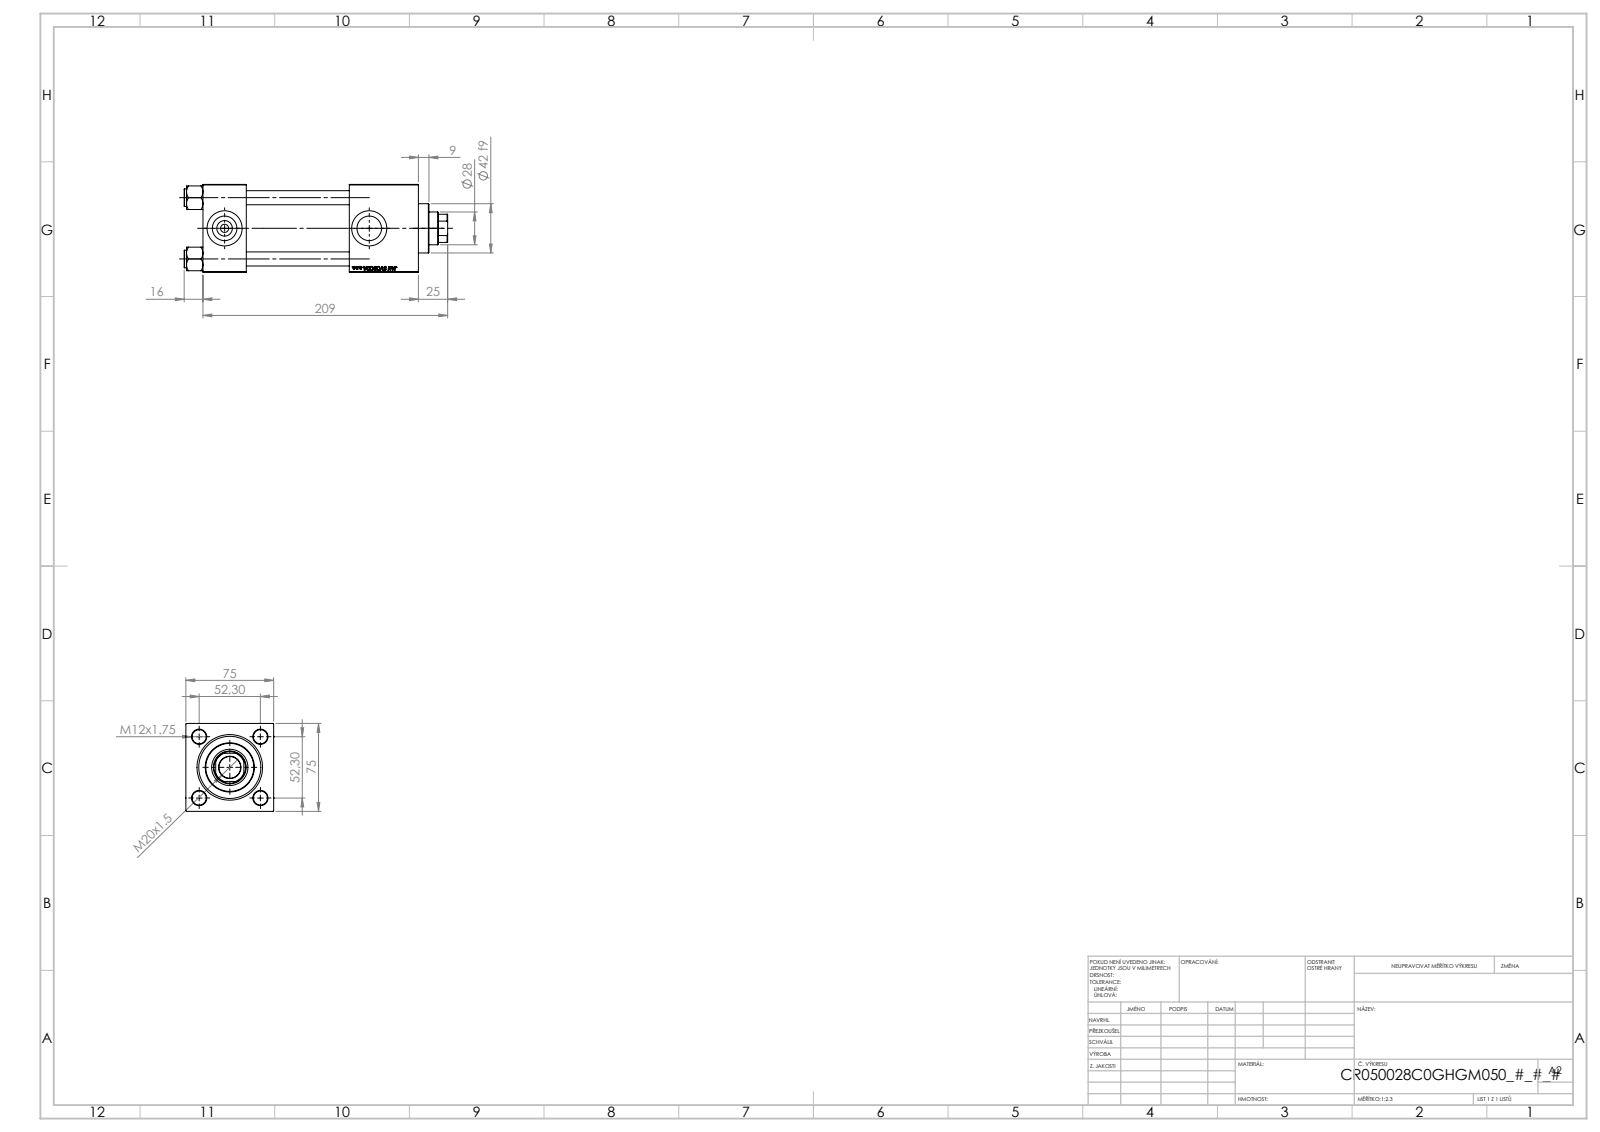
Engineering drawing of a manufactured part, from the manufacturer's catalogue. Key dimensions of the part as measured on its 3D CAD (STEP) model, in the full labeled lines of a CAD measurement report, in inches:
Part name (STEP PRODUCT): V215CR_C_Body; V215CR_C_TYCINKA; V215CR_VCP_C; V215_VC_A (+1 more)
STEP written by: SolidWorks 2019 (CONFIG_CONTROL_DESIGN)
Units: inches
Bodies: 11 solids, 1148 faces (526 planar, 86 cylindrical, 536 other)
Overall size (bounding box): 8.858 × 2.974 × 2.953
Volume: 43.7 in³ · Surface area: 260.5 in²
Round holes (diameter × count): ⌀0.472 ×4, ⌀0.276 ×2, ⌀0.825 ×2, ⌀1.181 ×2, ⌀0.728 ×1, ⌀1.102 ×1, ⌀1.22 ×1, ⌀1.614 ×1, ⌀1.969 ×1, ⌀2.087 ×1
Round bosses / shafts (diameter × count): ⌀0.591 ×4, ⌀2.205 ×1, ⌀1.654 ×1
Partial cylindrical surfaces — rounded edges, fillets, slot ends (radius × count): R0.531 ×1
Main face-to-face distances: 2.953, 1.457, 7.244, 5.787, 4.921, 3.465, 2.323, 6.114, 4.657, 1.193
Hole centre spacings: 1.456, 2.059, 2.912, 4.862
